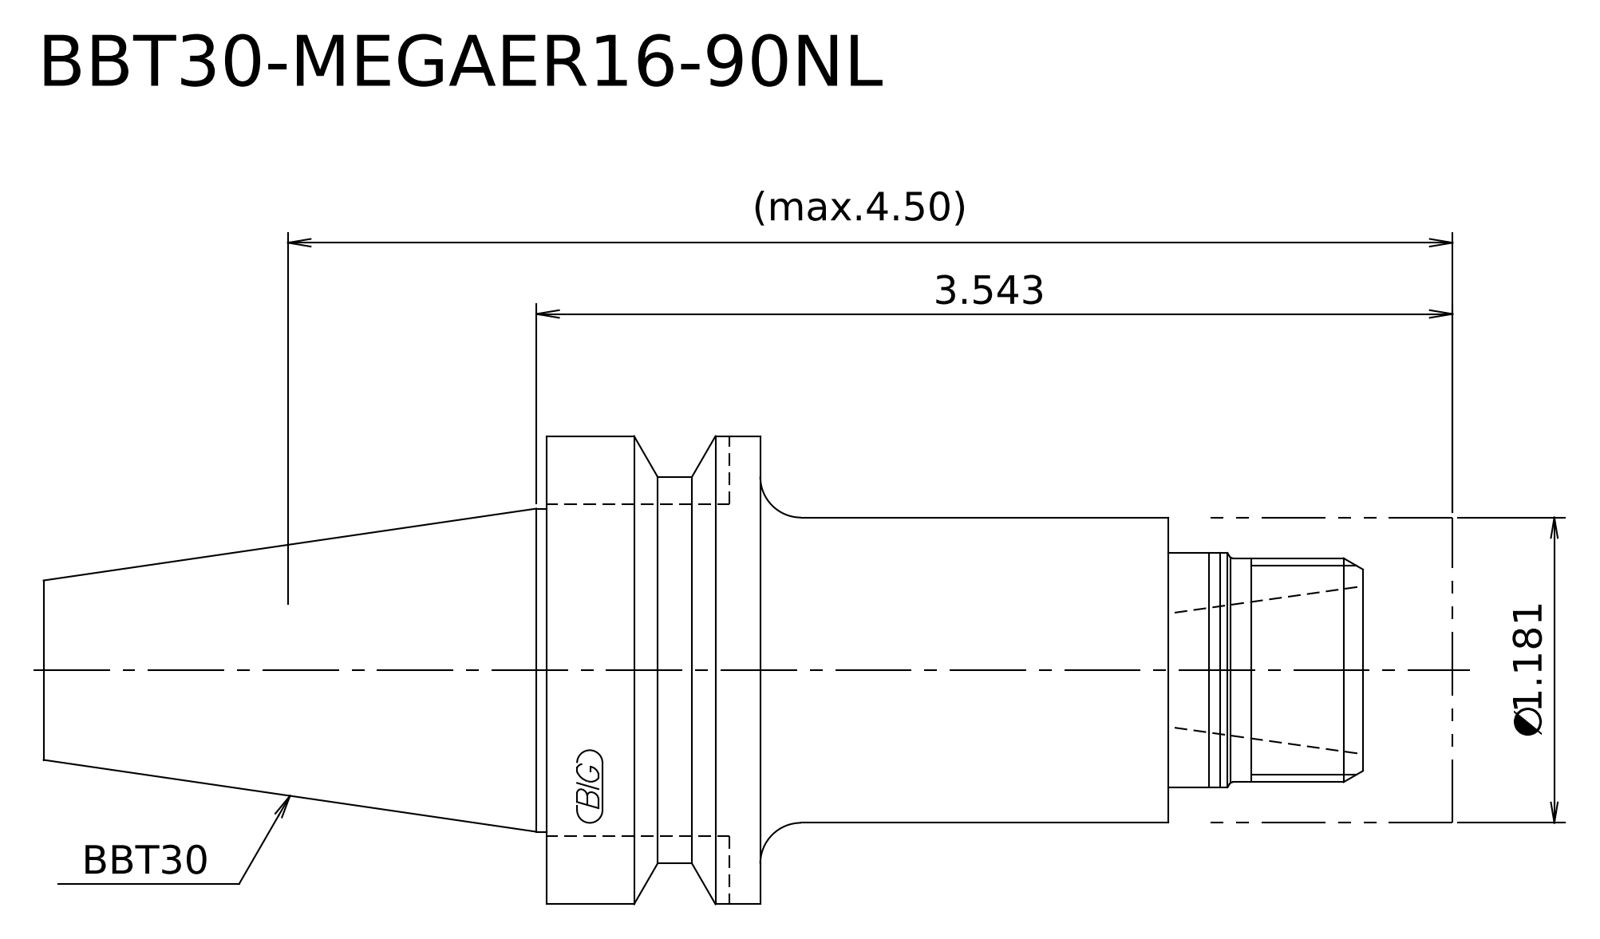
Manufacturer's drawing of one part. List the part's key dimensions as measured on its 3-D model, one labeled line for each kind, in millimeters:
STEP written by: Kubotek KeyCreator 2011 V10.0.2 (22737) (automotive_design)
Units: millimetres
Bodies: 2 solids, 21 faces (7 planar, 8 cylindrical, 6 other)
Overall size (bounding box): 138.4 × 46 × 46
Volume: 110 695 mm³ · Surface area: 18 785 mm²
Round bosses / shafts (diameter × count): ⌀46 ×1, ⌀38 ×1, ⌀31.75 ×1, ⌀30 ×1, ⌀23 ×1, ⌀22 ×1
Main face-to-face distances: 64, 25, 89, 68, 43, 21, 8.8, 16.2, 59.2, 80.2
